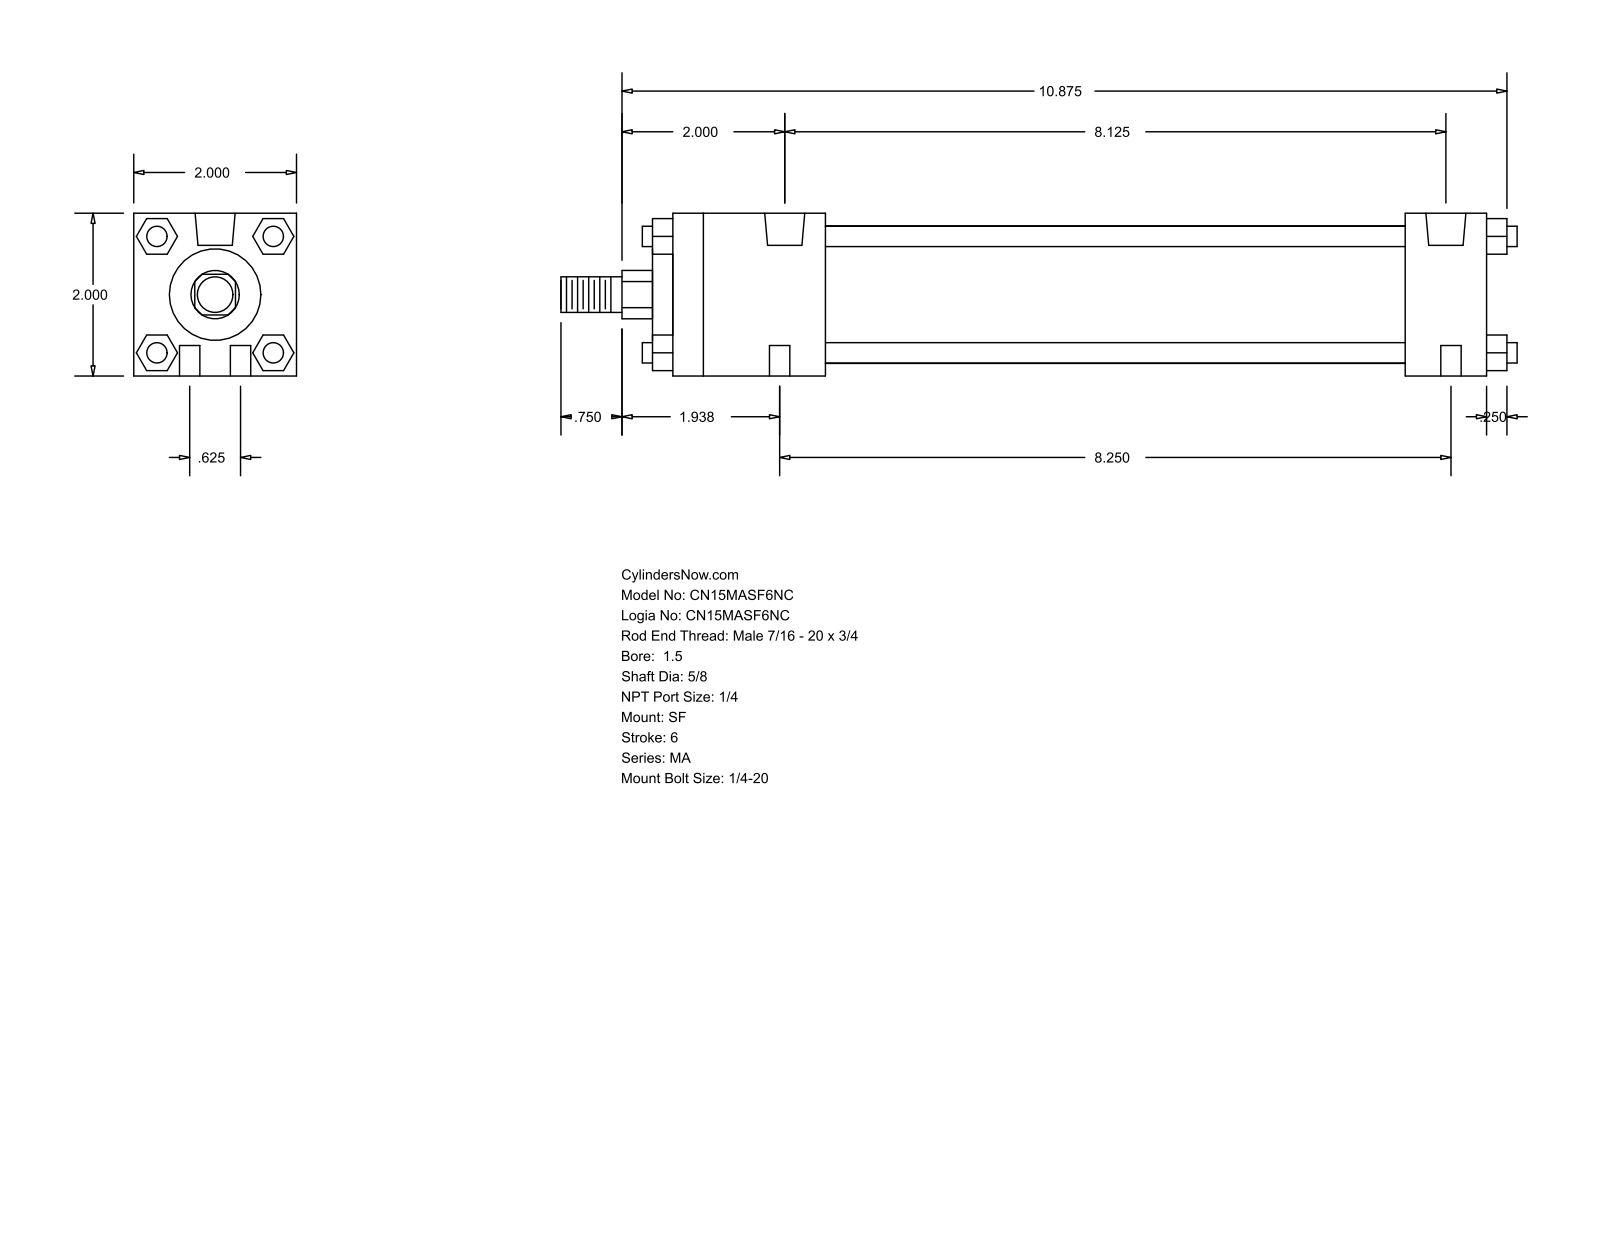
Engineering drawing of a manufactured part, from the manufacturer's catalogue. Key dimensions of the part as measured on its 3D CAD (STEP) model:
Part name (STEP PRODUCT): MA_SF__0150_0.625
STEP written by: GSSL Pune (CONFIG_CONTROL_DESIGN)
Units: millimetres
Bodies: 0 solids, 124 faces (94 planar, 30 cylindrical, 0 other)
Overall size (bounding box): 298.45 × 50.8 × 50.8
Round holes (diameter × count): ⌀6.35 ×4, ⌀7.94 ×2, ⌀12.49 ×2
Round bosses / shafts (diameter × count): ⌀6.35 ×4, ⌀42.93 ×1, ⌀28.57 ×1, ⌀15.88 ×1, ⌀11.11 ×1
Partial cylindrical surfaces — rounded edges, fillets, slot ends (radius × count): R7.54 ×1
Main face-to-face distances: 50.8, 254, 6.35, 260.35, 47.62, 228.59, 180.97, 206.38, 25.41, 53.97
Hole centre spacings: 8.1, 15.88, 206.38, 208.11, 208.12, 209.55, 210.15
